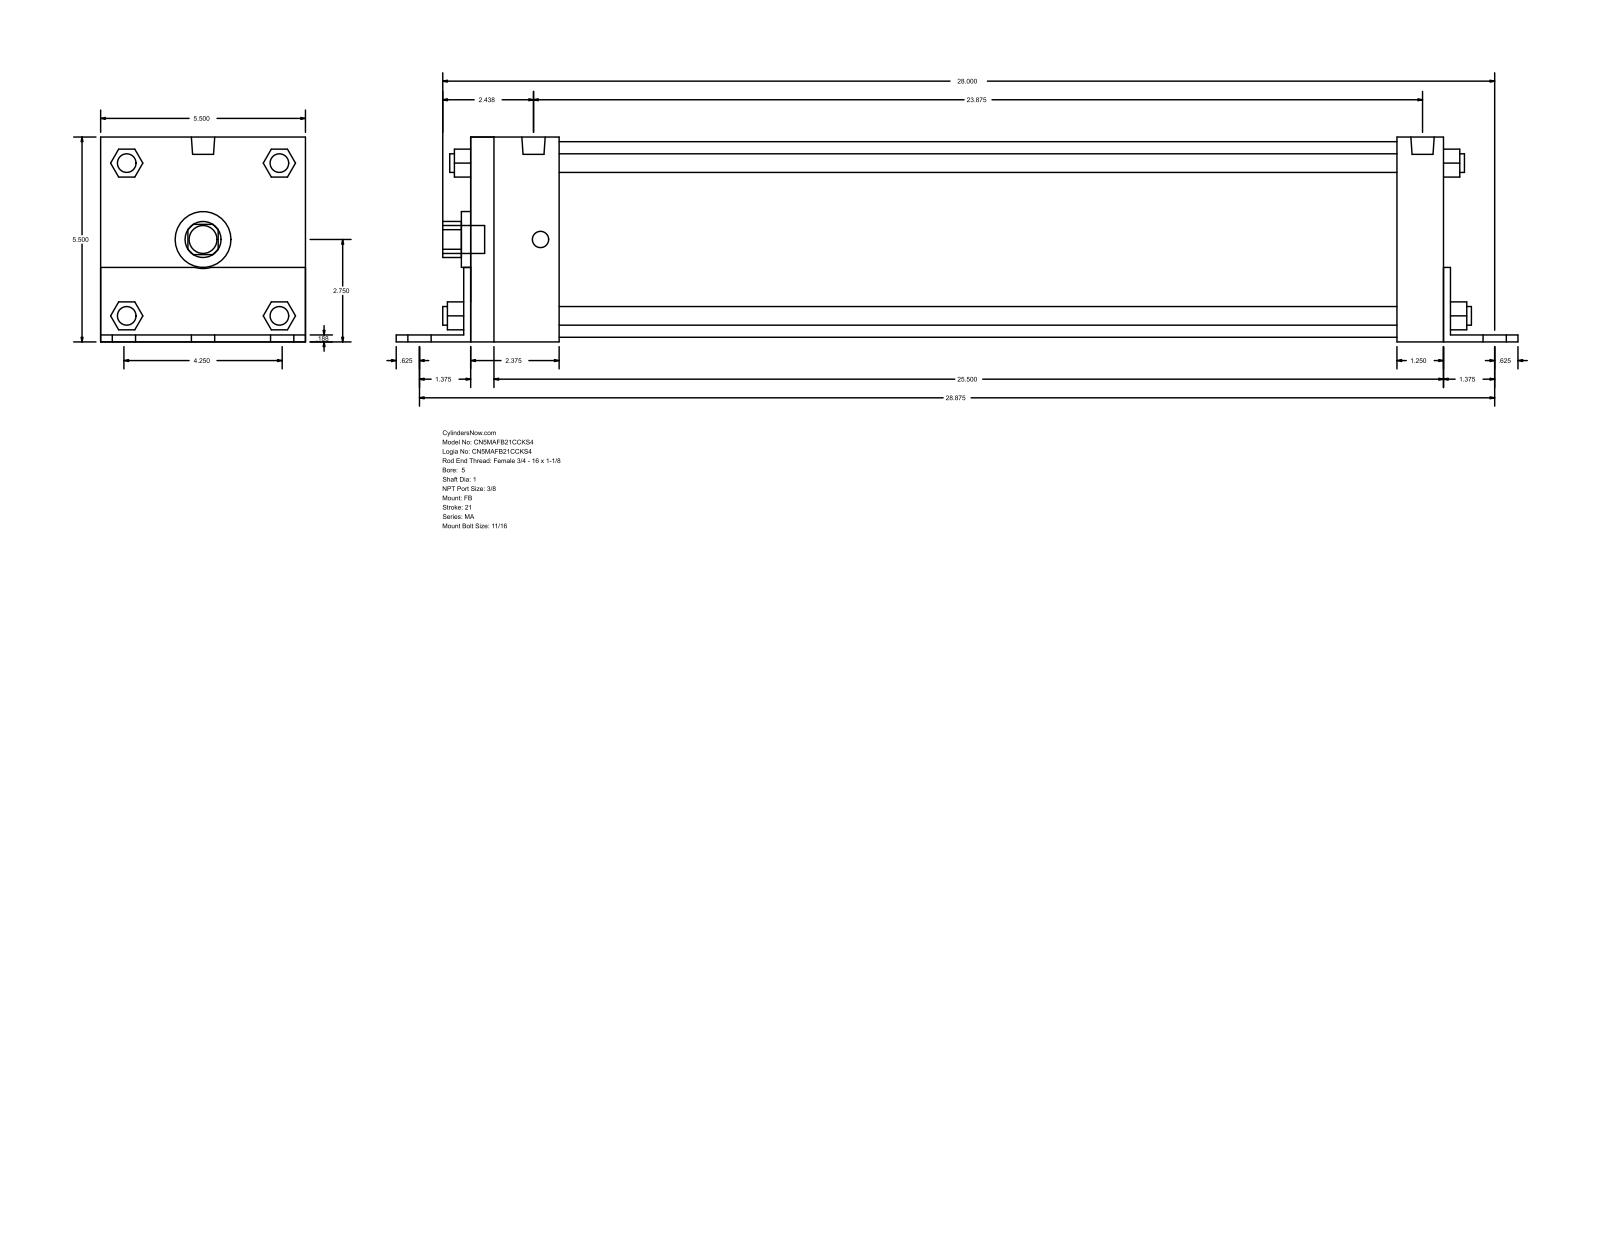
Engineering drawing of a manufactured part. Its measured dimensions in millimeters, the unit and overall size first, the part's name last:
Units: millimetres
Overall size (bounding box): 765.17 × 139.75 × 139.7
Round holes (diameter × count): ⌀25.4 ×1, ⌀38.1 ×1, ⌀133.35 ×1
Round bosses / shafts (diameter × count): ⌀17.46 ×6, ⌀12.7 ×4, ⌀11.11 ×4, ⌀15.93 ×2, ⌀19.05 ×1
Partial cylindrical surfaces — rounded edges, fillets, slot ends (radius × count): R12.29 ×1, R19.81 ×1
Main face-to-face distances: 139.7, 4.76, 139.75, 4.71, 134.99, 663.57, 4.77, 668.34, 673.1, 668.33
Bodies: 0 solids, 140 faces (105 planar, 35 cylindrical, 0 other)
Part name (STEP PRODUCT): MA_FB__0500_1
STEP written by: GSSL Pune (CONFIG_CONTROL_DESIGN)
